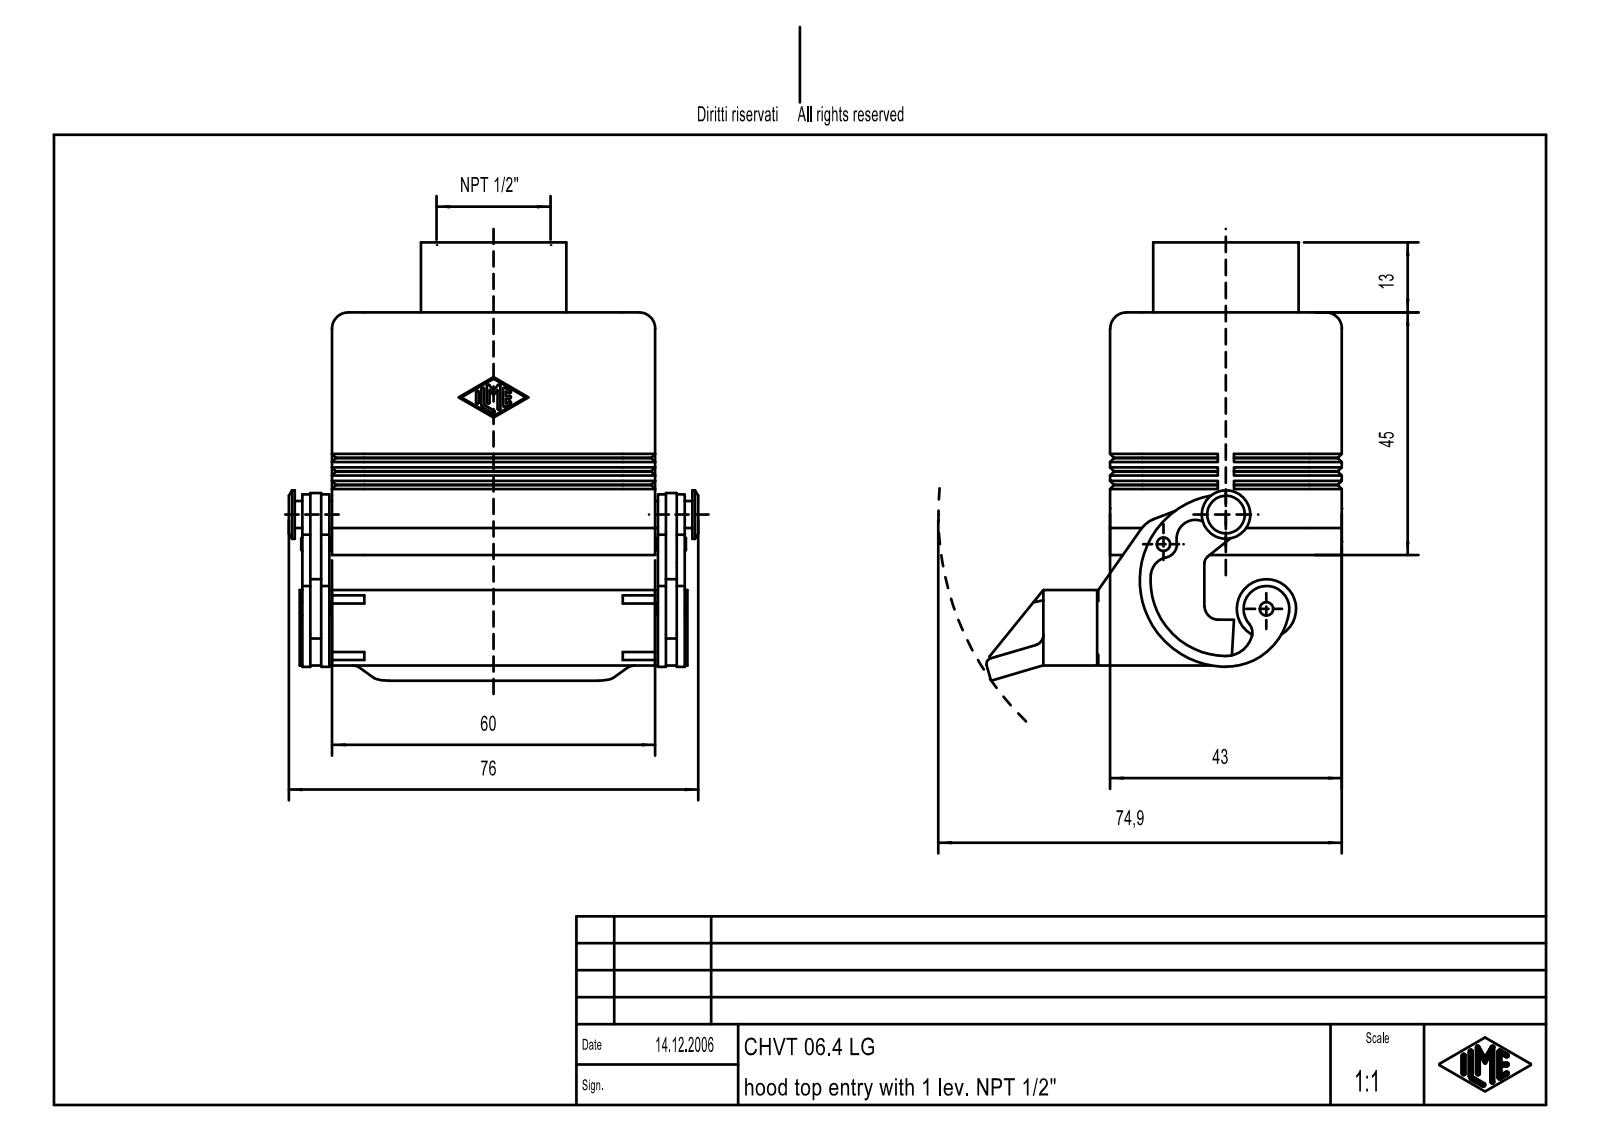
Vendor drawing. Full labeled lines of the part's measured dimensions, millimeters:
Part name (STEP PRODUCT): MSBO9285
STEP written by: Creo Elements/Direct Modeling 18.0B 02-Dec-2011 (C) Parametric Technology GmbH (AUTOMOTIVE_DESIGN)
Units: millimetres
Bodies: 1 solid, 465 faces (249 planar, 154 cylindrical, 62 other)
Overall size (bounding box): 81.32 × 76 × 65.99
Volume: 54 943 mm³ · Surface area: 32 818 mm²
Round holes (diameter × count): ⌀4 ×4, ⌀2.46 ×2, ⌀2.46 ×2, ⌀2.5 ×1
Round bosses / shafts (diameter × count): ⌀27 ×1, ⌀11 ×1, ⌀9 ×1, ⌀5 ×1, ⌀2 ×1
Partial cylindrical surfaces — rounded edges, fillets, slot ends (radius × count): R0.25 ×14, R2 ×7, R3 ×6, R3 ×4, R5.3 ×4, R6 ×4, R2.5 ×3, R1 ×2
Main face-to-face distances: 3, 40, 2, 4, 8.5, 37, 57, 11.5, 43, 66
Hole centre spacings: 27, 44, 51.62
